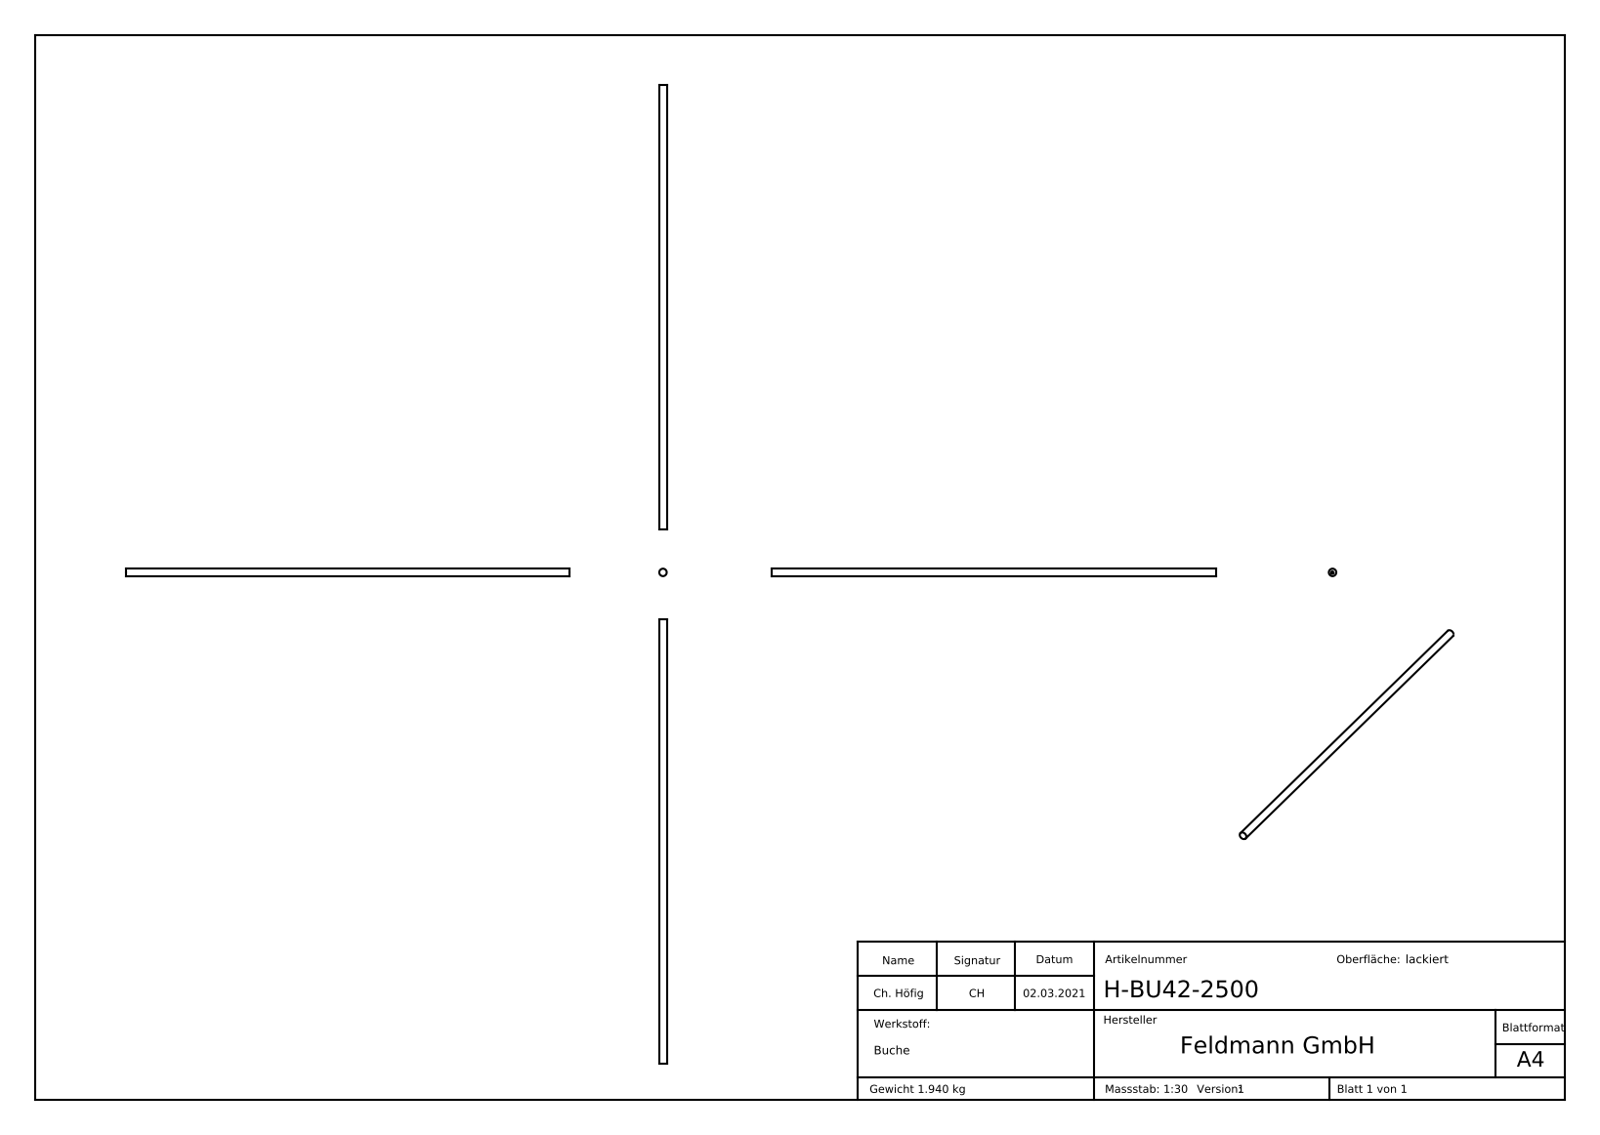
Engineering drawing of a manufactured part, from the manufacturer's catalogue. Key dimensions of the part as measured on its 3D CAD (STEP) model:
Part name (STEP PRODUCT): H-BU42-2500
STEP written by: SolidWorks 2018 (CONFIG_CONTROL_DESIGN)
Units: millimetres
Bodies: 1 solid, 294 faces (170 planar, 2 cylindrical, 122 other)
Overall size (bounding box): 2500 × 42 × 42
Volume: 3 464 000 mm³ · Surface area: 332 652 mm²
Round bosses / shafts (diameter × count): ⌀42 ×1
Main face-to-face distances: 2500, 2499.9, 3.07, 2.23, 1.49, 4.61, 1.12, 3.2, 1.19, 3.78
